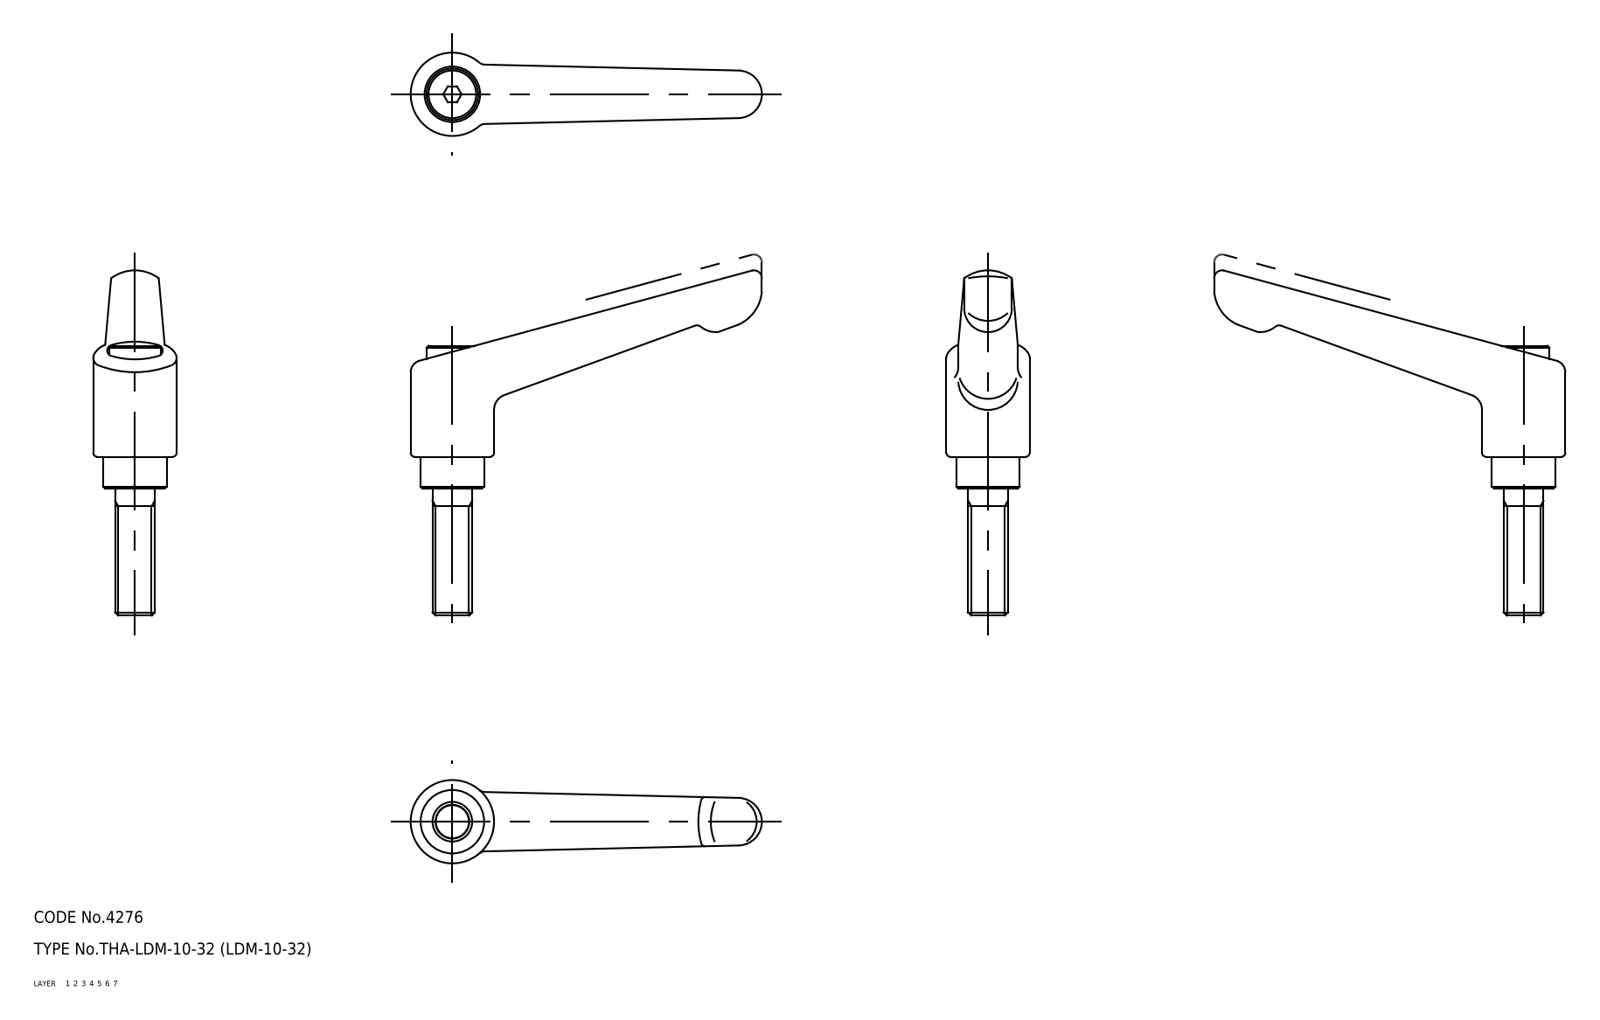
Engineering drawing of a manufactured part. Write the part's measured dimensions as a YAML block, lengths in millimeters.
part_name: "sleeve; screw; handle; LDM_10_32_26016_36"
step_written_by: "CADfix (AUTOMOTIVE_DESIGN)"
units: millimeters
bodies: {solids: 3, faces: 75, planar: 0, cylindrical: 0, other: 75}
overall_size: [88.5, 87, 21]
volume: 21870
surface_area: 9335
